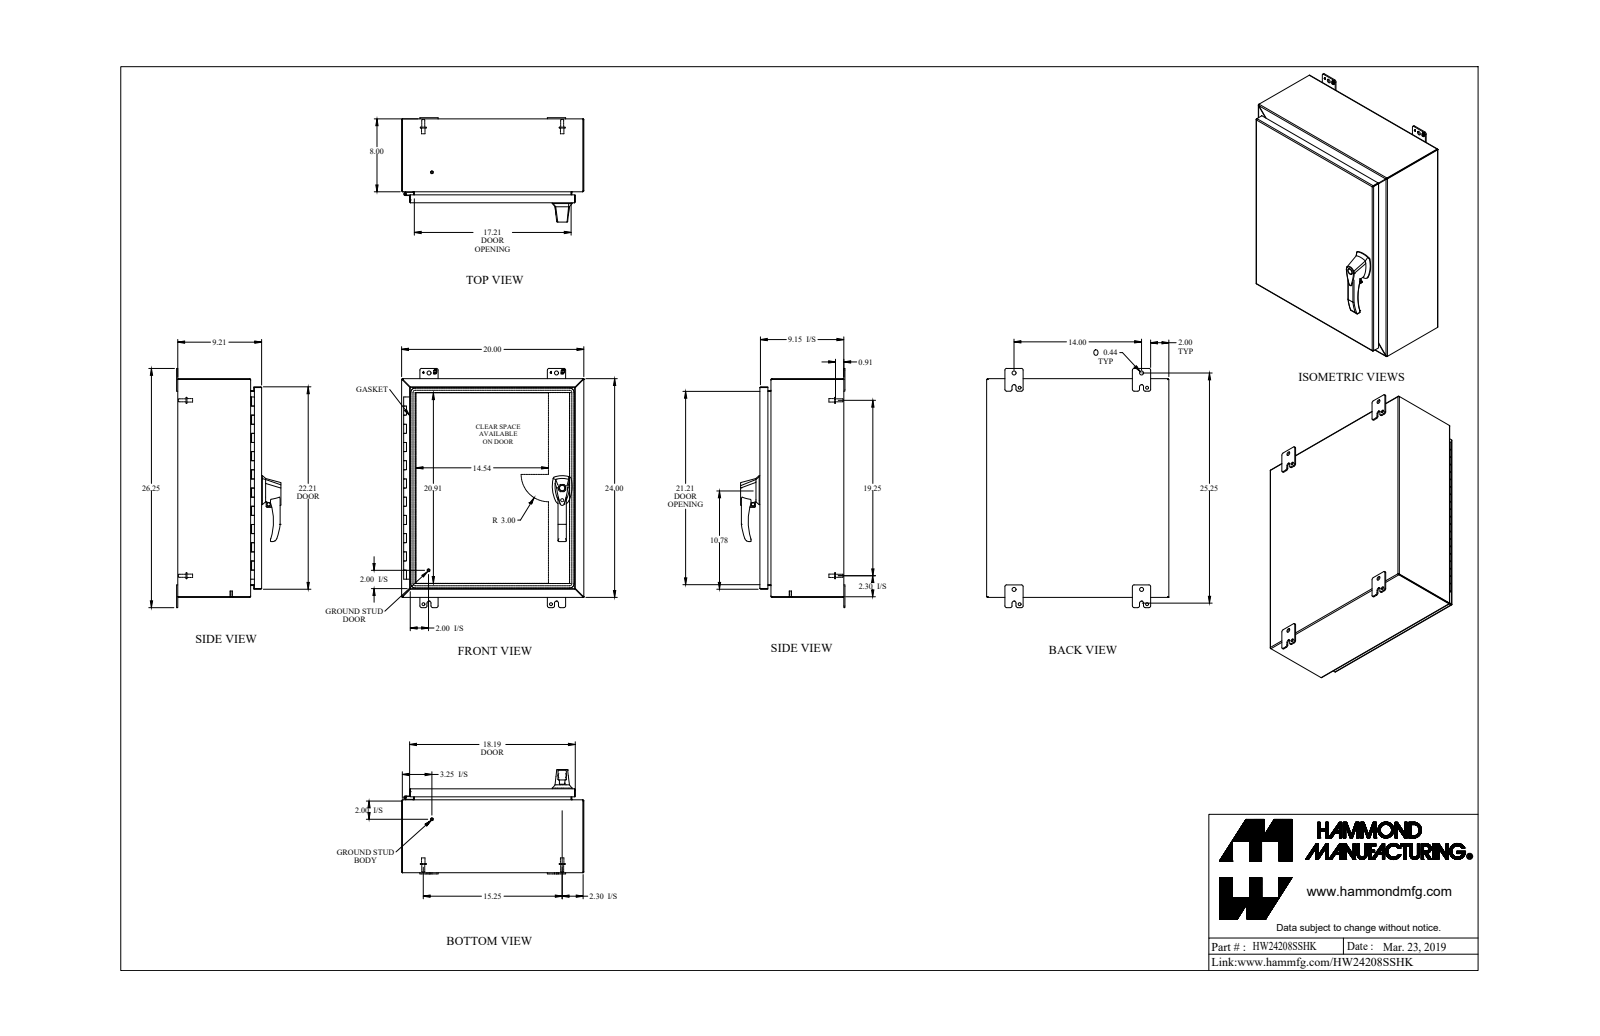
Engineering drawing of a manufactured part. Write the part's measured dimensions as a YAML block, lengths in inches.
part_name: "HW24208SSHK"
step_written_by: "SolidWorks 2018 (AUTOMOTIVE_DESIGN)"
units: inches
bodies: {solids: 46, faces: 1423, planar: 699, cylindrical: 569, other: 155}
overall_size: [26.25, 20, 11.45]
volume: 166
surface_area: 4234
round_holes:
  - {diameter: 0.176, count: 6}
  - {diameter: 0.313, count: 5}
  - {diameter: 0.25, count: 3}
  - {diameter: 0.265, count: 3}
  - {diameter: 0.413, count: 3}
  - {diameter: 0.196, count: 2}
  - {diameter: 0.256, count: 2}
  - {diameter: 0.394, count: 2}
  - {diameter: 0.437, count: 2}
  - {diameter: 0.187, count: 1}
  - {diameter: 0.233, count: 1}
  - {diameter: 0.33, count: 1}
round_bosses_or_shafts:
  - {diameter: 0.375, count: 9}
  - {diameter: 0.25, count: 7}
  - {diameter: 0.156, count: 6}
  - {diameter: 0.65, count: 4}
  - {diameter: 0.332, count: 4}
  - {diameter: 0.313, count: 4}
  - {diameter: 1, count: 3}
  - {diameter: 0.51, count: 3}
partial_cylinders:
  - {radius: 0.25, count: 27}
  - {radius: 0.188, count: 24}
  - {radius: 0.036, count: 20}
  - {radius: 0.108, count: 20}
  - {radius: 0.06, count: 12}
  - {radius: 0.125, count: 9}
  - {radius: 0.045, count: 8}
  - {radius: 0.218, count: 8}
face_to_face_distances: [0.072, 9.138, 9.066, 0.072, 9.138, 9.21, 19.928, 23.928, 7.928, 19.856]
hole_center_spacings: [1.111, 8.118, 8.119, 16.237, 1.338, 6.78, 7.576, 7.577]
